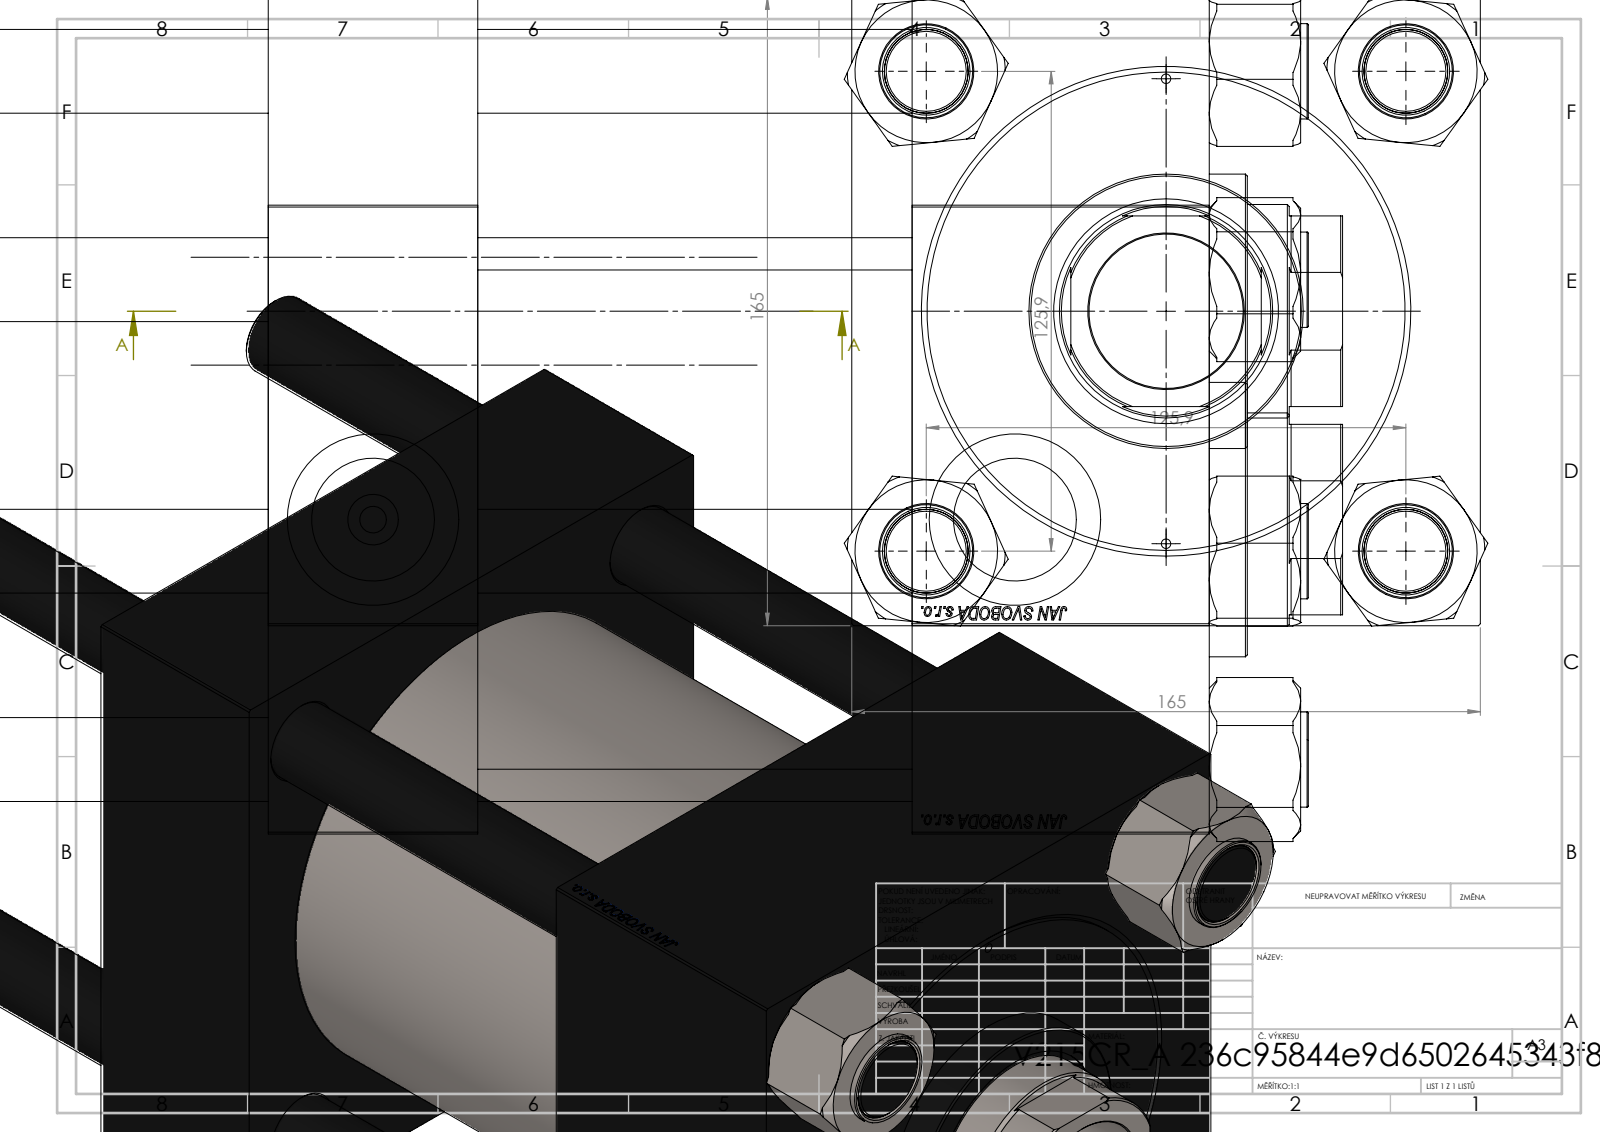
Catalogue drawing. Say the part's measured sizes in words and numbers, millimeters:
The part is named "V215CR_BODY_A; V215_VC_A; NUT_M5; CR025_012_A_0_G_A_G_M_020_+#_##_TYCINKA (+1 more)". Its 3-D file was written by "SolidWorks 2019 (CONFIG_CONTROL_DESIGN)". It is 11 solids with 1188 faces: 570 planar, 82 cylindrical and 536 other. Overall it measures 363 by 168.94 by 165.27 millimeters. Its volume is 4 836 000 cubic millimeters and its surface area 586 426 square millimeters. Round holes: 4 of diameter 22, 2 of diameter 2.5, 2 of diameter 7, 2 of diameter 32.24, 2 of diameter 45, 1 of diameter 40.5, 1 of diameter 56, 1 of diameter 59, 1 of diameter 96, 1 of diameter 125, 1 of diameter 125.5. Round bosses or shafts: 4 of diameter 25, 1 of diameter 131, 1 of diameter 72. Partial cylindrical surfaces (rounded edges, fillets, slot ends): 1 of radius 27. The main face-to-face distances are 165, 55, 247, 192, 114, 169, 78, 163.3, 218.3, 49.3. The hole center spacings are 62.98, 89.02, 125.9, 139.02, 61, 178.05, 122, 168.5.
